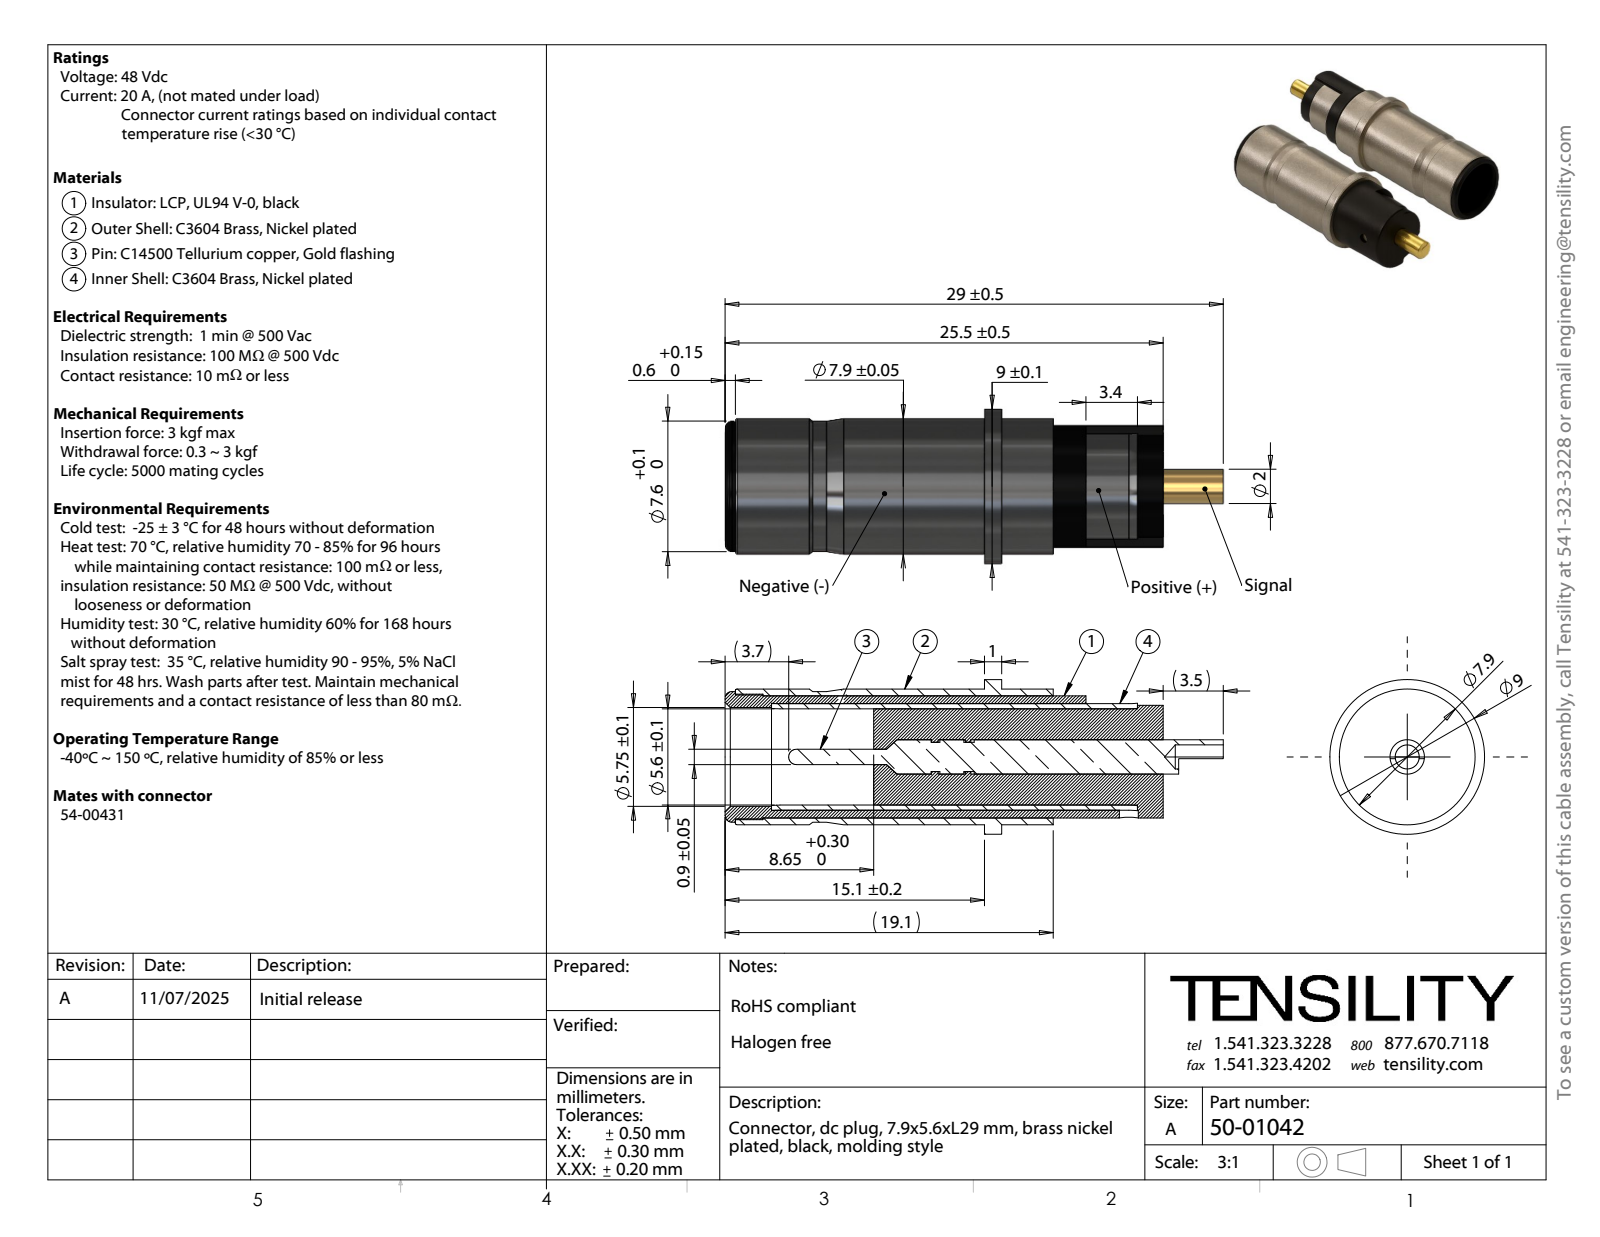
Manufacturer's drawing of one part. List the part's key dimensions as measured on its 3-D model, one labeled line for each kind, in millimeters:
Part name (STEP PRODUCT): H679-290-A____-0.STEP; 50-01042; H679-290-A____.STEP; H679-290____.STEP (+2 more)
STEP written by: SolidWorks 2025 (AUTOMOTIVE_DESIGN)
Units: millimetres
Bodies: 4 solids, 115 faces (29 planar, 60 cylindrical, 26 other)
Overall size (bounding box): 29 × 9 × 9
Volume: 967 mm³ · Surface area: 3 312 mm²
Round holes (diameter × count): ⌀0.9 ×1, ⌀1.1 ×1, ⌀1.4 ×1, ⌀1.7 ×1, ⌀2 ×1, ⌀5.6 ×1, ⌀5.75 ×1, ⌀7.1 ×1, ⌀7.2 ×1
Round bosses / shafts (diameter × count): ⌀9 ×1, ⌀7.9 ×1, ⌀7.6 ×1, ⌀7.3 ×1, ⌀6.2 ×1
Partial cylindrical surfaces — rounded edges, fillets, slot ends (radius × count): R3 ×1
Main face-to-face distances: 16.85, 6.45, 9.4, 10.4, 1, 7.45, 3, 4.9, 1.5, 12.4
